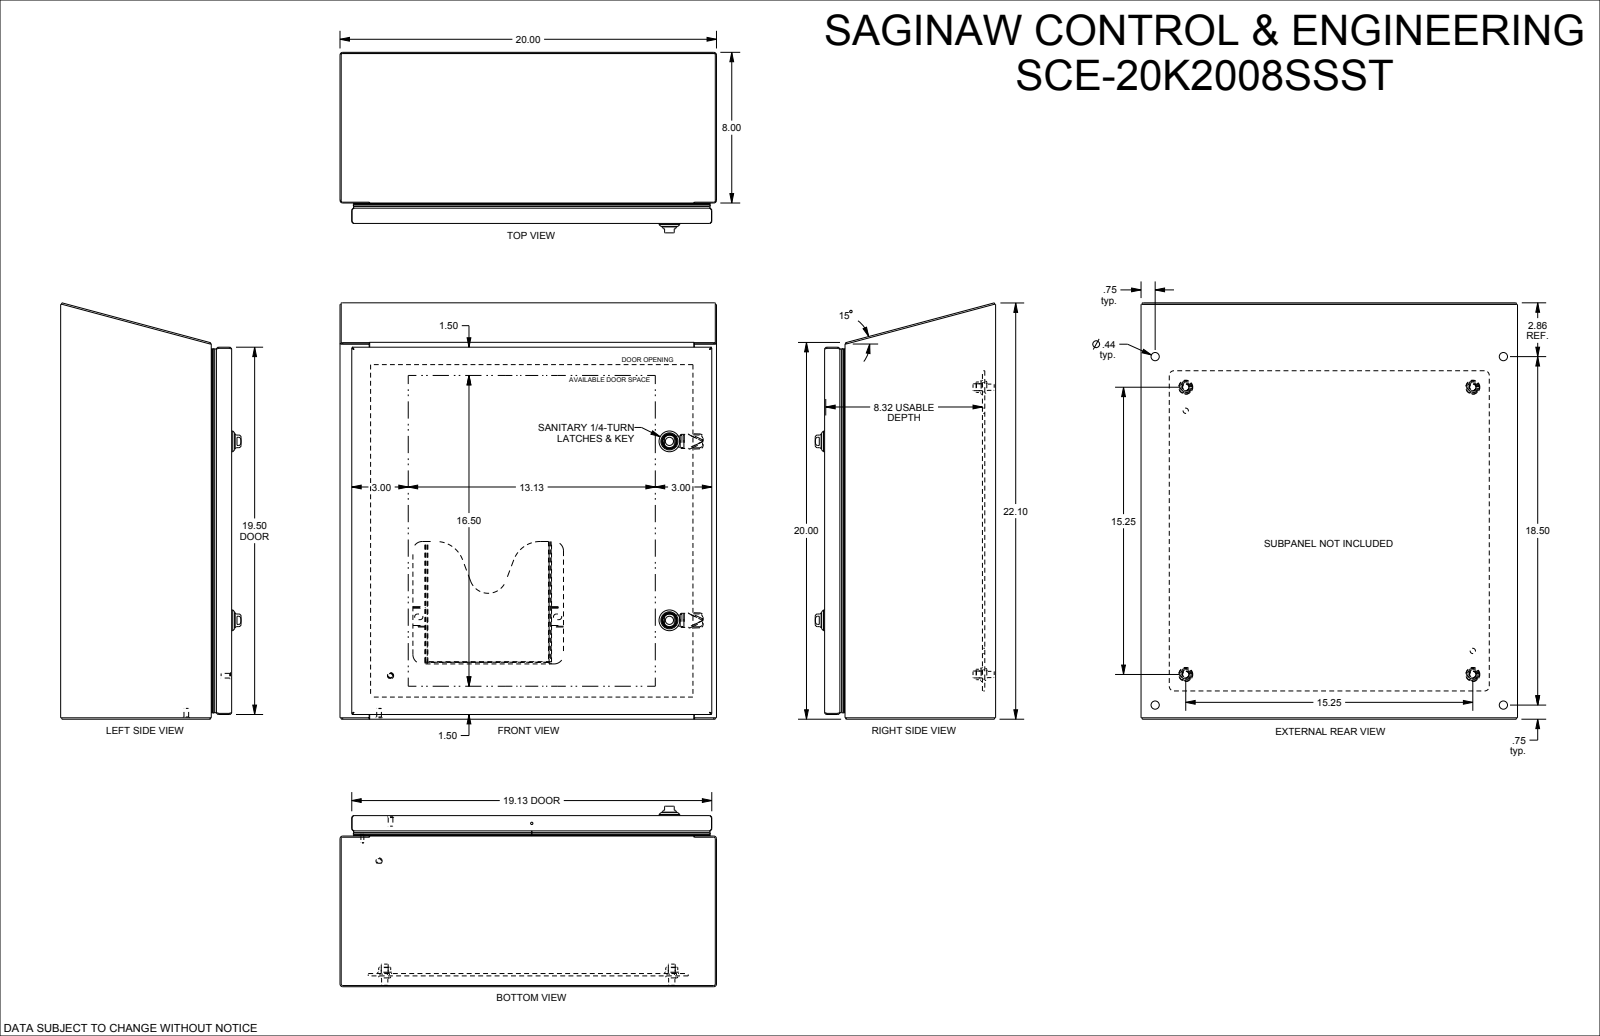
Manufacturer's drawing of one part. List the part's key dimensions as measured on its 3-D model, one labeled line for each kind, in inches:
Part name (STEP PRODUCT): SCE-20K2008SSST
STEP written by: SolidWorks 2021 (AUTOMOTIVE_DESIGN)
Units: inches
Bodies: 52 solids, 3118 faces (1124 planar, 736 cylindrical, 1258 other)
Overall size (bounding box): 22.106 × 20 × 9.584
Volume: 195.9 in³ · Surface area: 4 599 in²
Round holes (diameter × count): ⌀0.156 ×4, ⌀0.201 ×4, ⌀0.25 ×4, ⌀0.367 ×4, ⌀0.437 ×4, ⌀0.5 ×4, ⌀0.197 ×2, ⌀0.266 ×2, ⌀0.281 ×2, ⌀0.315 ×2, ⌀0.394 ×2, ⌀0.41 ×2
Round bosses / shafts (diameter × count): ⌀0.248 ×6, ⌀0.563 ×4, ⌀0.366 ×4, ⌀0.332 ×4, ⌀0.156 ×4, ⌀0.196 ×3, ⌀1.102 ×2, ⌀0.906 ×2
Partial cylindrical surfaces — rounded edges, fillets, slot ends (radius × count): R0.03 ×64, R0.01 ×28, R0.029 ×24, R0.02 ×22, R0.04 ×21, R0.25 ×20, R0.05 ×16, R0.07 ×14
Main face-to-face distances: 0.075, 0.06, 9.024, 8.949, 9.084, 9.009, 19.925, 0.5, 0.625, 0.125
Hole centre spacings: 16.953, 1.769, 2.298, 15.25, 18.5, 23.865, 10.5, 0.985
